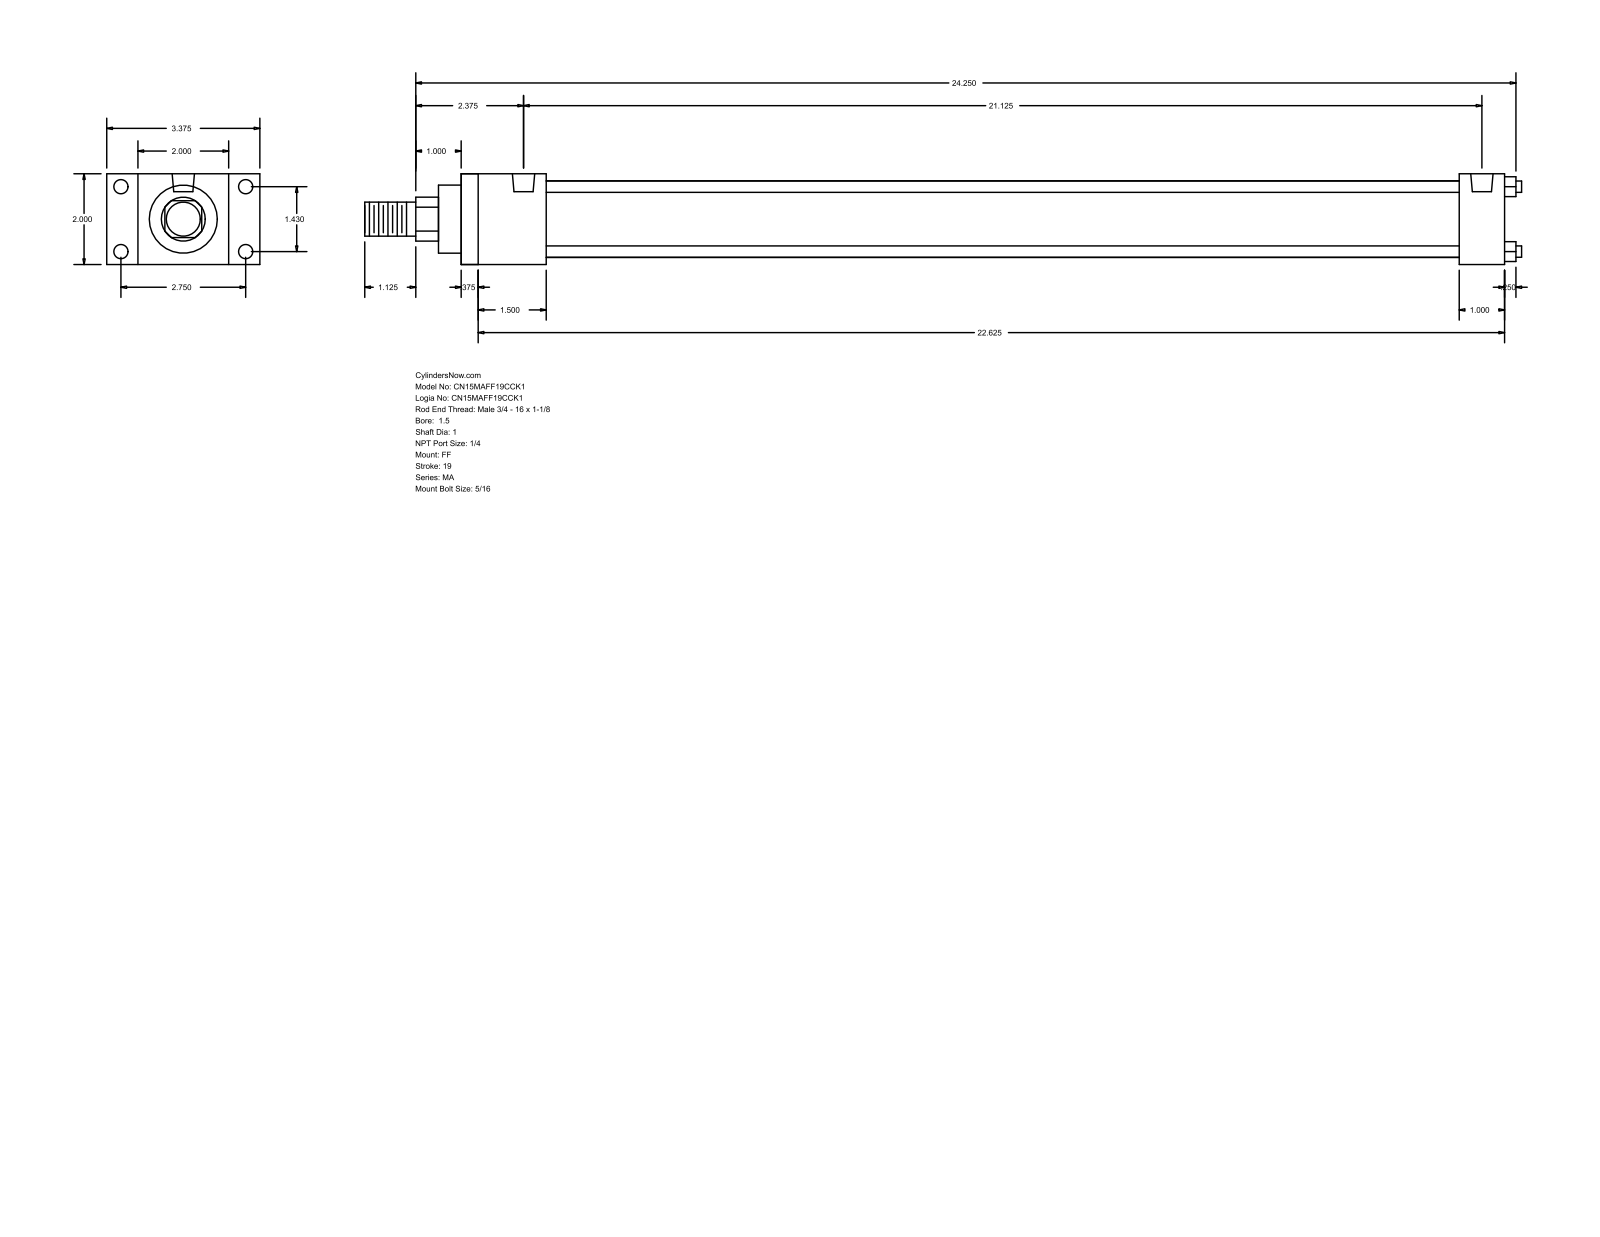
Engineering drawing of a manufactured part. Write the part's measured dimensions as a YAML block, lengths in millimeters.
part_name: "MA_FF__0150_1"
step_written_by: "GSSL Pune (CONFIG_CONTROL_DESIGN)"
units: millimeters
bodies: {solids: 0, faces: 92, planar: 64, cylindrical: 28, other: 0}
overall_size: [647.7, 85.72, 50.8]
round_holes:
  - {diameter: 7.94, count: 8}
  - {diameter: 12.49, count: 2}
round_bosses_or_shafts:
  - {diameter: 6.35, count: 4}
  - {diameter: 42.93, count: 1}
  - {diameter: 38.1, count: 1}
  - {diameter: 25.4, count: 1}
  - {diameter: 19.05, count: 1}
partial_cylinders:
  - {radius: 12.29, count: 1}
face_to_face_distances: [50.8, 584.2, 9.52, 574.68, 25.4, 47.63, 558.8, 38.11, 549.28, 511.17]
hole_center_spacings: [36.32, 69.84, 78.72, 536.57]
